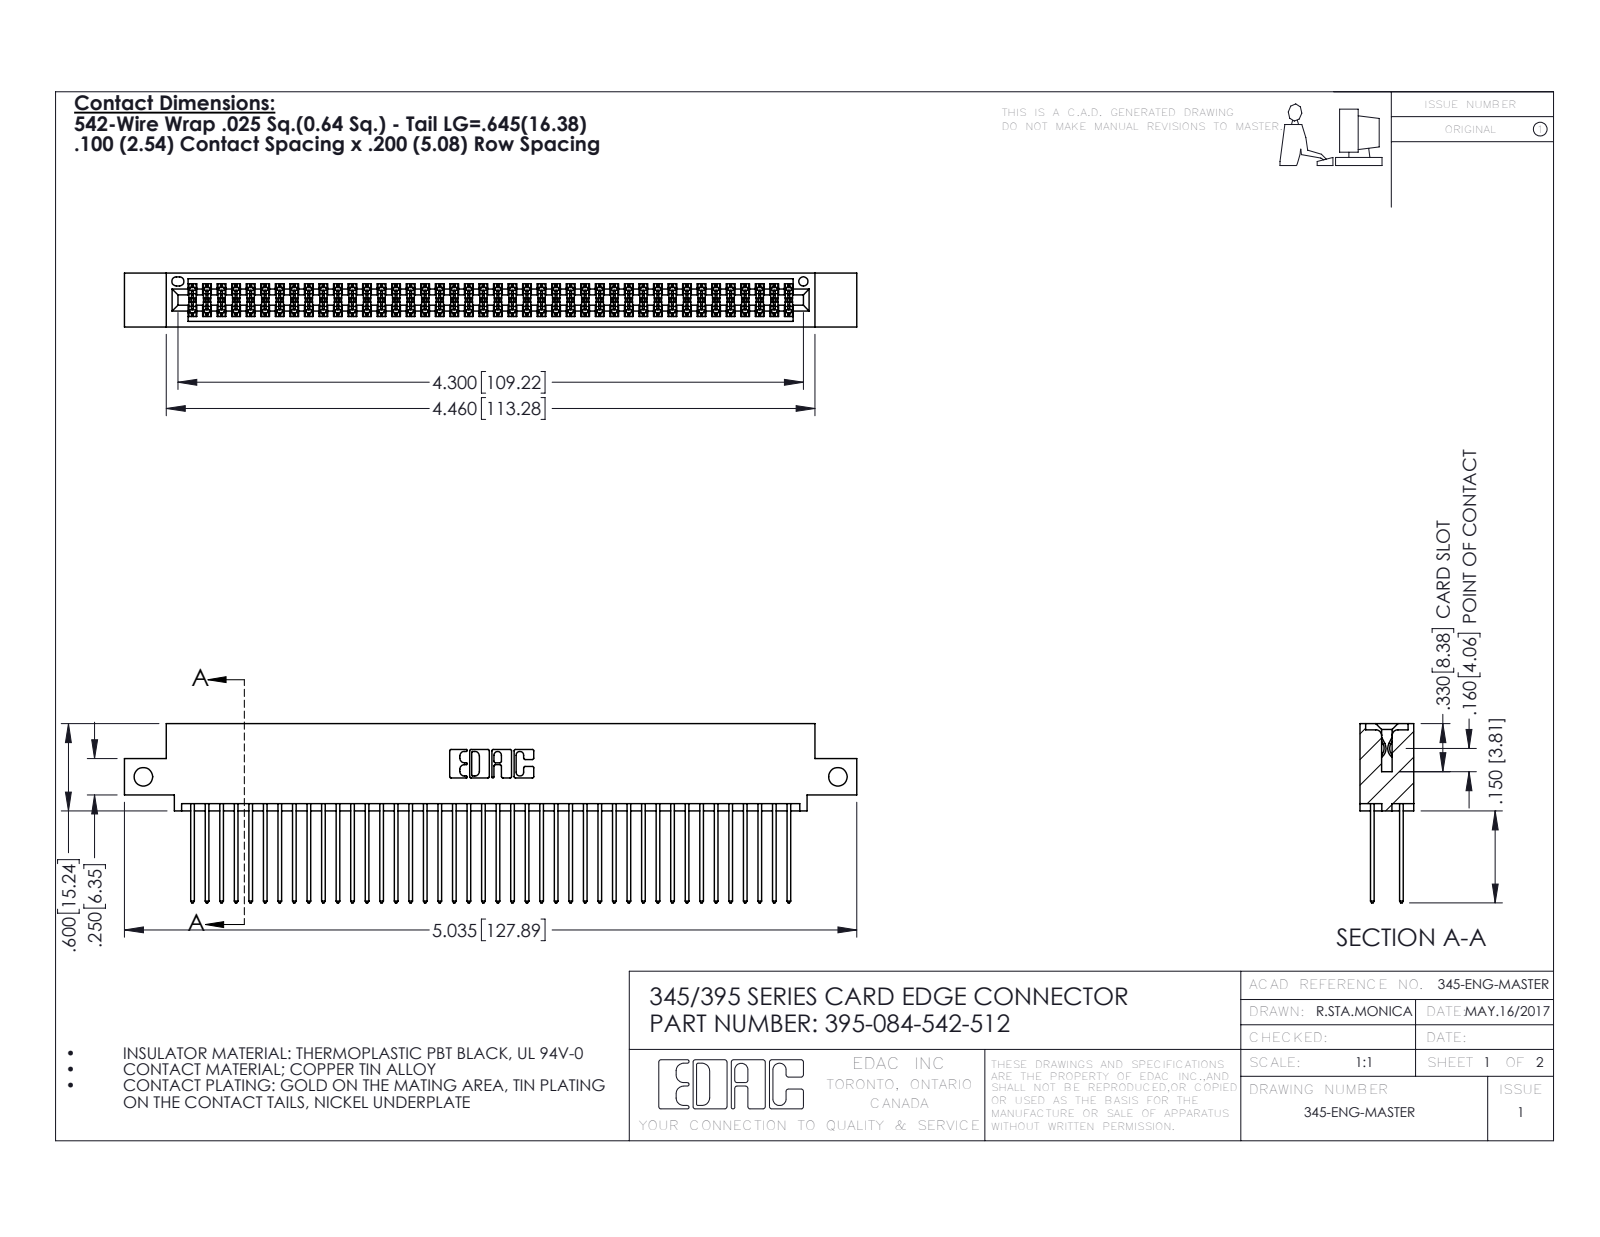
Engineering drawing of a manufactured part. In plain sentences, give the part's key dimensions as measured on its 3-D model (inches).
The part is named "345-292-001_345-293-142; 395-084-542-512; 345 Part_0.110 Offset - Side Mount". Its 3-D file was written by "SolidWorks 2016 (CONFIG_CONTROL_DESIGN)". It is 85 solids with 4330 faces: 2856 planar, 1474 cylindrical and 0 other. Overall it measures 5.035 by 1.232 by 0.37 inches. Its volume is 0.772 cubic inches and its surface area 31.76 square inches. Round holes: 2 of diameter 0.128, 1 of diameter 0.064. Partial cylindrical surfaces (rounded edges, fillets, slot ends): 126 of radius 0.006, 84 of radius 0.01, 22 of radius 0.01, 6 of radius 0.007, 6 of radius 0.031, 3 of radius 0.026, 2 of radius 0.014, 2 of radius 0.019. The main face-to-face distances are 0.298, 0.072, 0.2, 0.098, 0.272, 0.025, 0.225, 0.37, 0.175, 0.149. The hole center spacings are 4.775.
